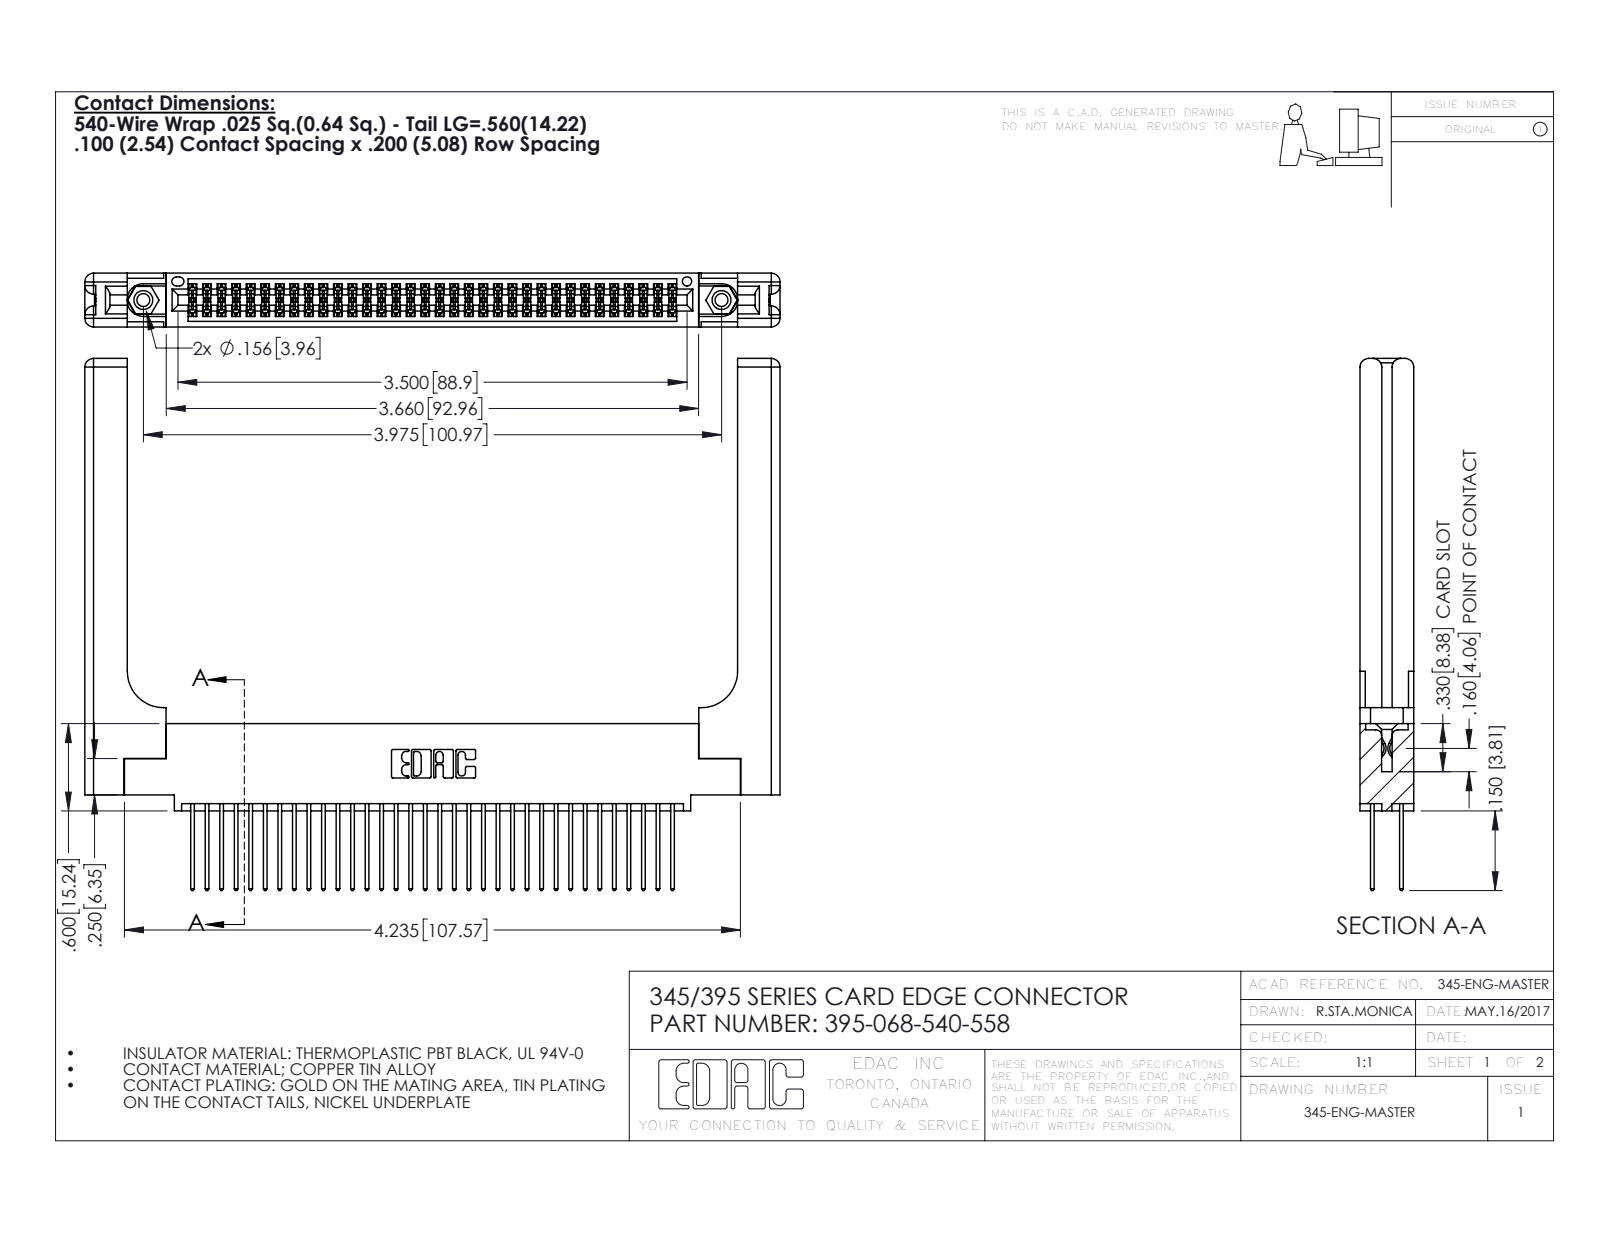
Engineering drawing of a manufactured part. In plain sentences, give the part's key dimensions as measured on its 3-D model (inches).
The part is named "345-250-001_345-250-001-102; 395-068-540-558; 345-292-001_345-293-140; 345-220-058_345-220-058 (+1 more)". Its 3-D file was written by "SolidWorks 2016 (CONFIG_CONTROL_DESIGN)". It is 73 solids with 3786 faces: 2476 planar, 1250 cylindrical and 60 other. Overall it measures 4.779 by 3.657 by 0.37 inches. Its volume is 1.243 cubic inches and its surface area 36.87 square inches. Round holes: 2 of diameter 0.089, 2 of diameter 0.125, 2 of diameter 0.156, 1 of diameter 0.064. Round bosses or shafts: 2 of diameter 0.155. Partial cylindrical surfaces (rounded edges, fillets, slot ends): 102 of radius 0.006, 68 of radius 0.01, 22 of radius 0.01, 16 of radius 0.06, 6 of radius 0.007, 6 of radius 0.031, 3 of radius 0.026, 2 of radius 0.014. The main face-to-face distances are 0.072, 0.298, 0.37, 0.2, 0.098, 0.272, 0.025, 0.225, 0.148, 0.15. The hole center spacings are 0.27, 3.74, 3.975.
